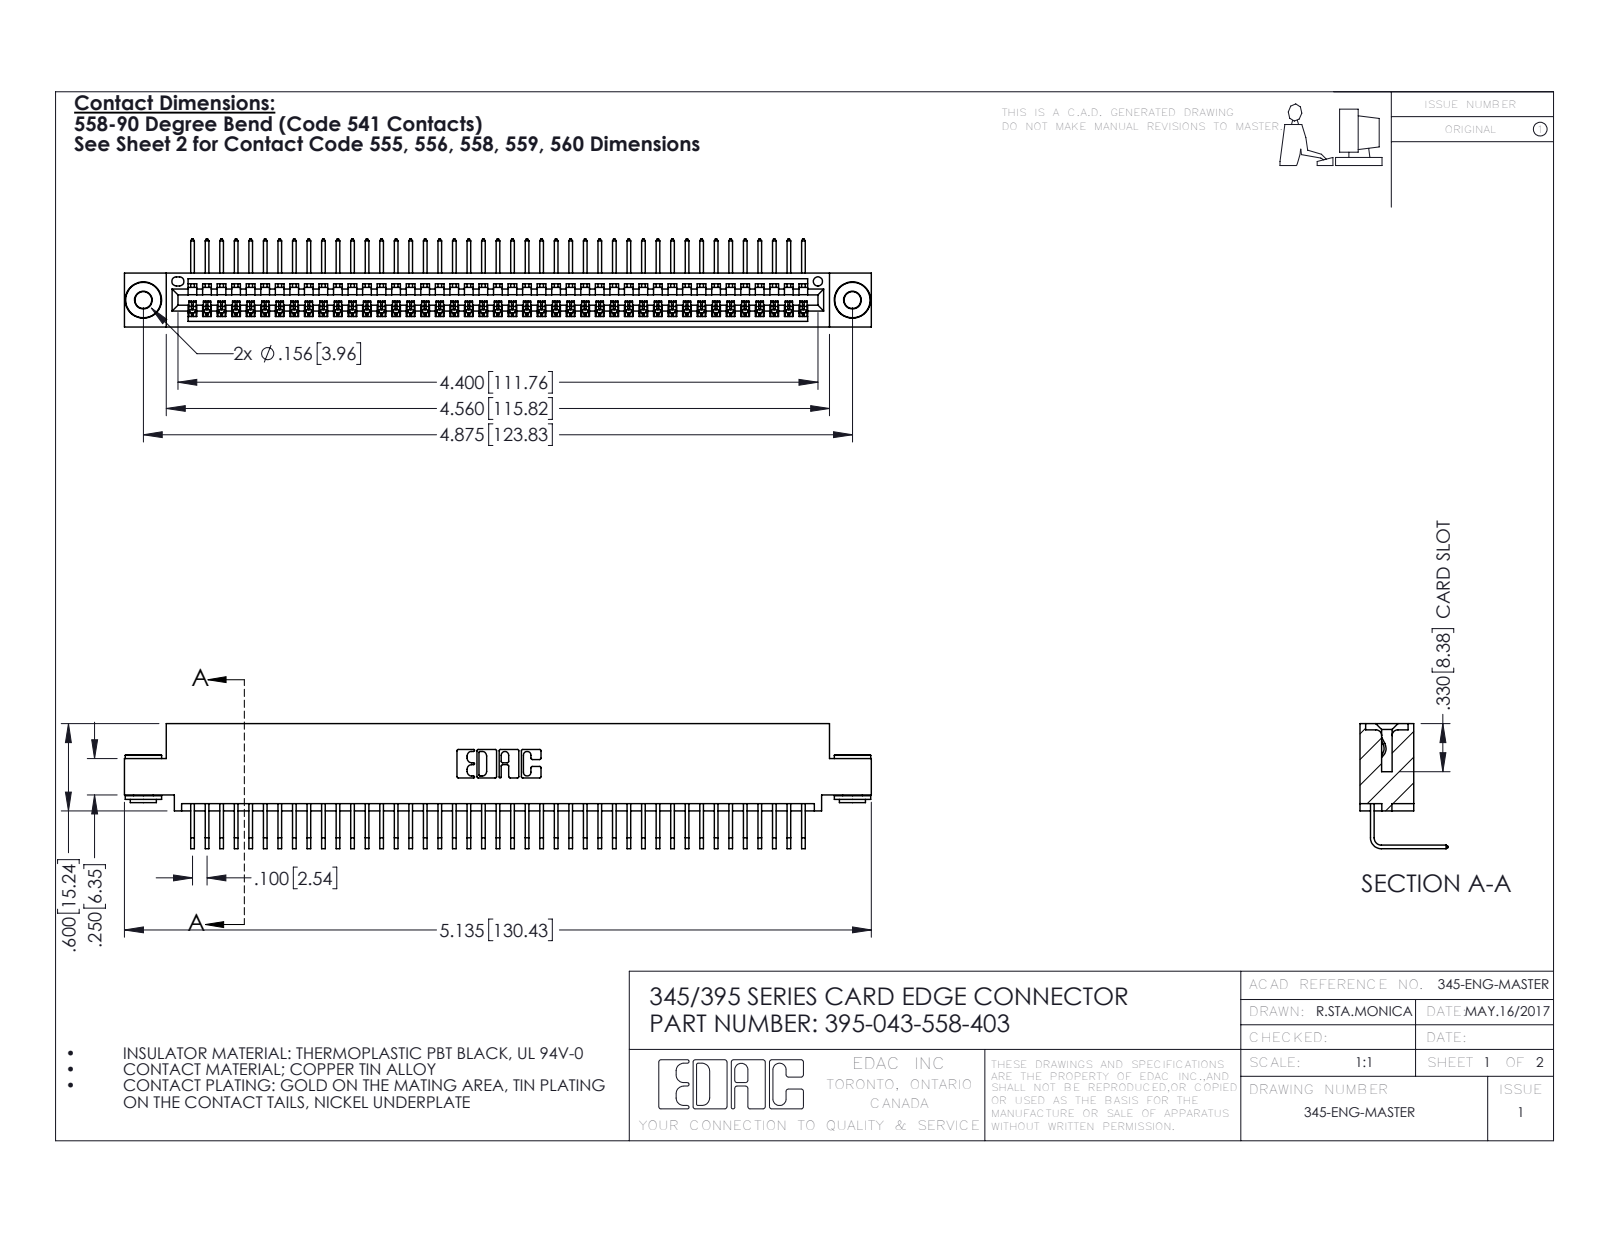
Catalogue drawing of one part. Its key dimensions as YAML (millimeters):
part_name: "395-043-558-403; 345-292-001_558 Tail - 2; 345-250-002_345-250-002-102; 345 Part_0.110 Offset - 0.156 Dia-TH"
step_written_by: "SolidWorks 2016 (CONFIG_CONTROL_DESIGN)"
units: millimeters
bodies: {solids: 46, faces: 2748, planar: 1900, cylindrical: 840, other: 8}
overall_size: [130.4, 21.8, 15.4]
volume: 12500
surface_area: 17740
round_holes:
  - {diameter: 2.9, count: 2}
  - {diameter: 4, count: 2}
  - {diameter: 1.6, count: 1}
round_bosses_or_shafts:
  - {diameter: 6.4, count: 2}
  - {diameter: 4.6, count: 2}
  - {diameter: 3.5, count: 2}
partial_cylinders:
  - {radius: 0.2, count: 86}
  - {radius: 0.3, count: 22}
  - {radius: 0.2, count: 6}
  - {radius: 0.8, count: 6}
  - {radius: 0.7, count: 3}
  - {radius: 0.8, count: 2}
  - {radius: 1, count: 2}
  - {radius: 0.4, count: 1}
face_to_face_distances: [1.8, 7.6, 9.4, 0.6, 5.1, 2.5, 6.9, 5.7, 3.8, 1.8]
hole_center_spacings: [6.9, 117.8, 123.8]
